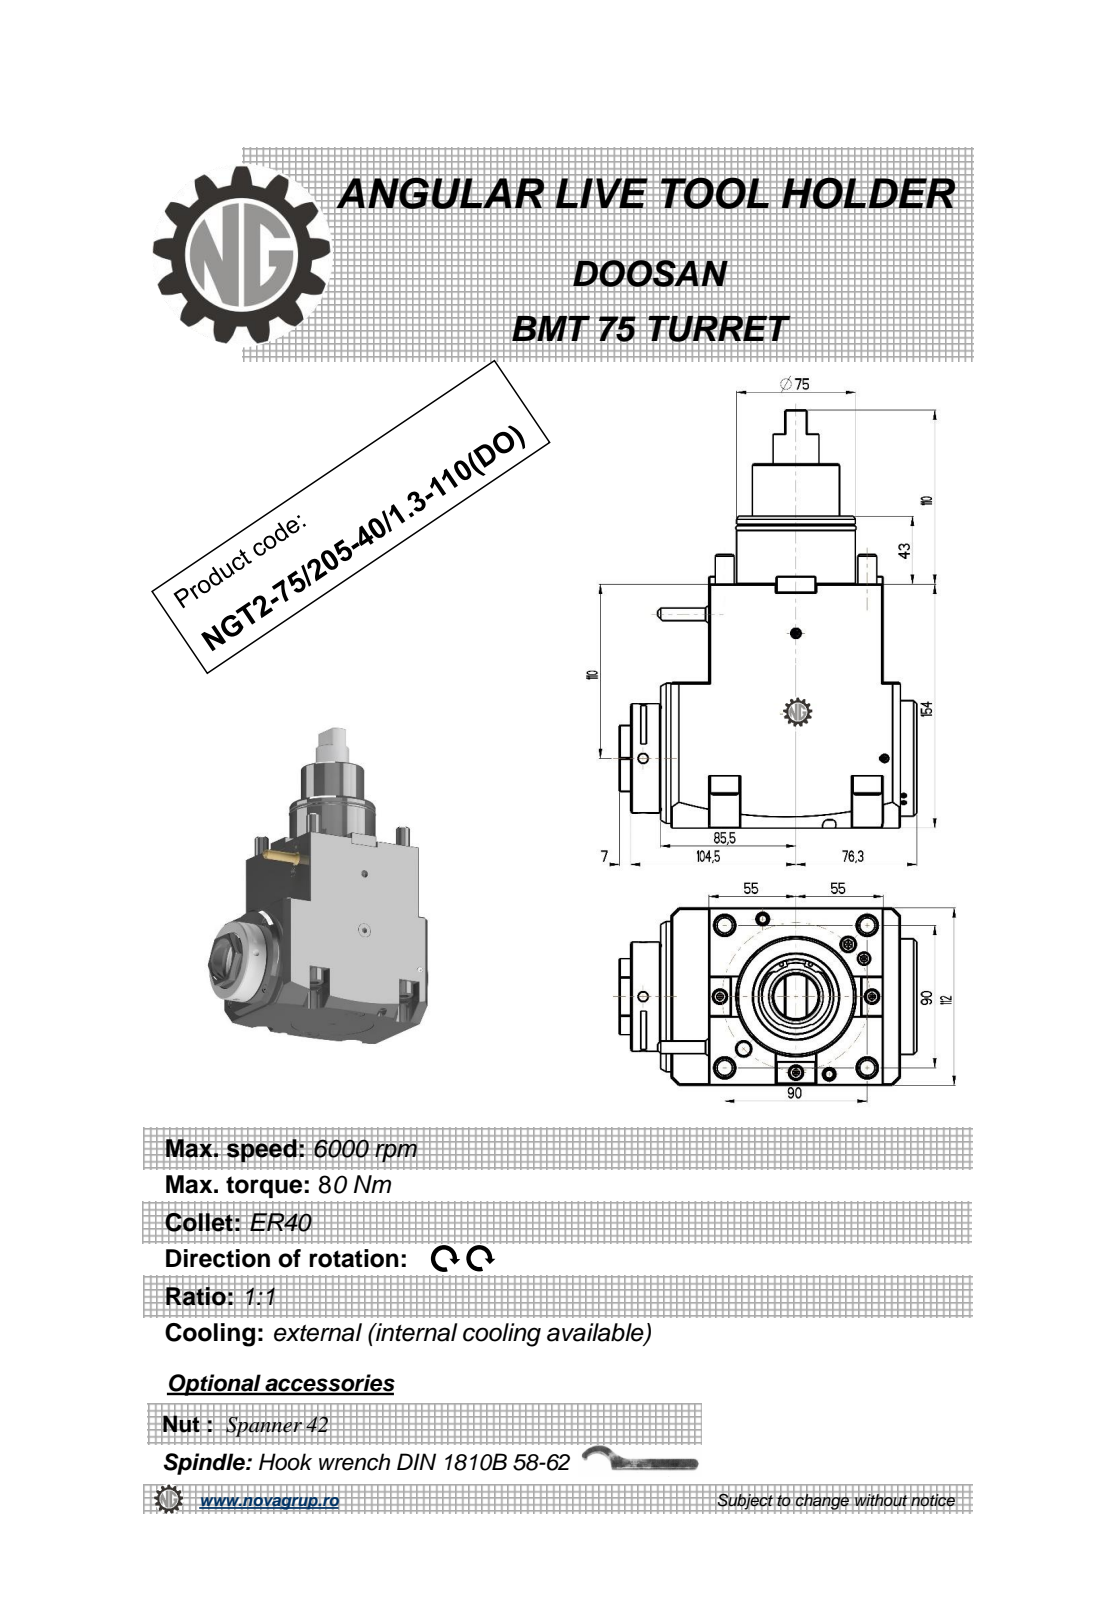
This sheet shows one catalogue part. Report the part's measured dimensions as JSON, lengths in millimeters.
{"part_name": "NGT2_75_205_40_1_3_110_DO", "step_written_by": "PRO/ENGINEER BY PARAMETRIC TECHNOLOGY CORPORATION, 2010280 (CONFIG_CONTROL_DESIGN)", "units": "millimeters", "bodies": {"solids": 2, "faces": 301, "planar": 151, "cylindrical": 73, "other": 77}, "overall_size": [264, 187.8, 112], "volume_mm3": 2660000, "surface_area_mm2": 150806, "round_holes": [[6, 2], [8.5, 2], [3, 1], [5, 1], [36.2, 1]], "round_bosses_or_shafts": [[18, 4], [12, 4], [95, 1], [75, 1], [74, 1], [73, 1], [70, 1], [69, 1]], "partial_cylinders_radius": [[9.5, 4], [0.8, 2], [350, 2], [24, 1]], "face_to_face_distances": [112, 110, 154, 121, 11, 62, 92, 30.5, 131.3, 21.3], "hole_center_spacings": [71.56, 93.34, 96.46, 133.64]}
